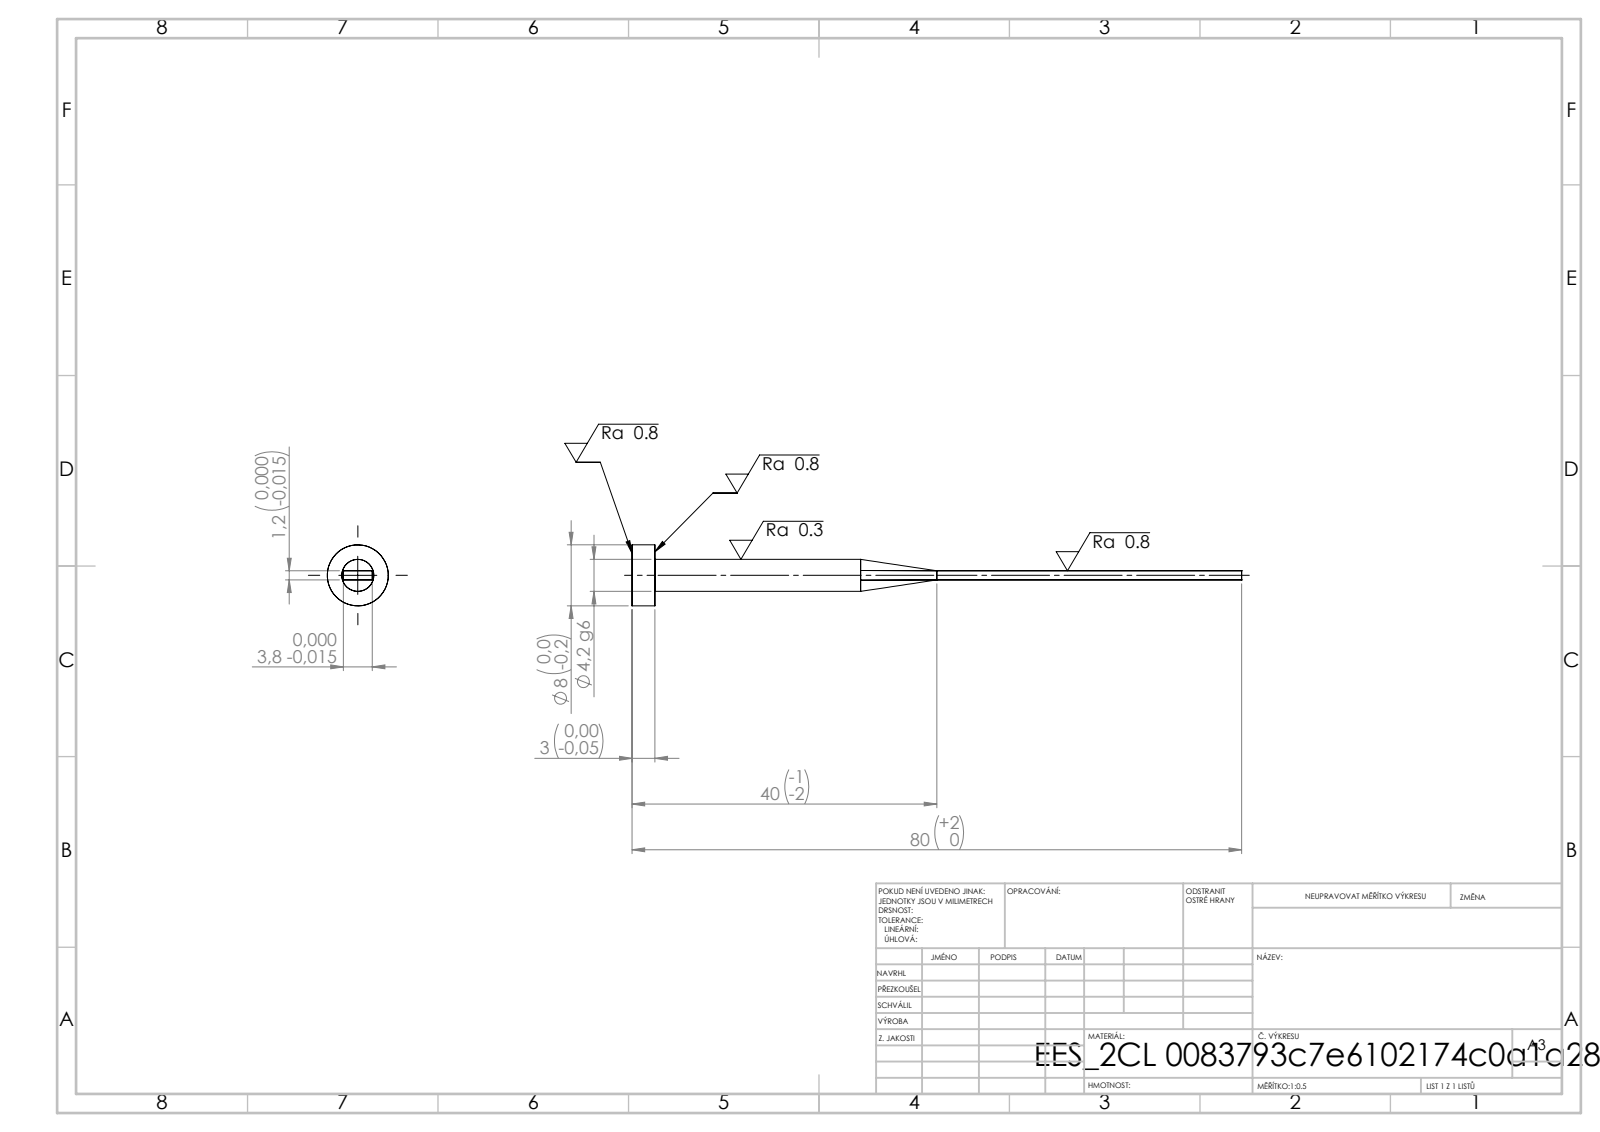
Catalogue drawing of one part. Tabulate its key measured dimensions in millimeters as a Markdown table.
| quantity | value |
| --- | --- |
| STEP written by | SolidWorks 2019 (CONFIG_CONTROL_DESIGN) |
| units | millimeters |
| bodies | 1 solid, 15 faces (7 planar, 4 cylindrical, 4 other) |
| overall size | 80 × 8 × 8 |
| volume | 796 mm³ |
| surface area | 1 035 mm² |
| round bosses / shafts (diameter × count) | 8 × 1, 4.2 × 1 |
| main face-to-face distances | 1.2, 3.8, 3, 80, 77 |
